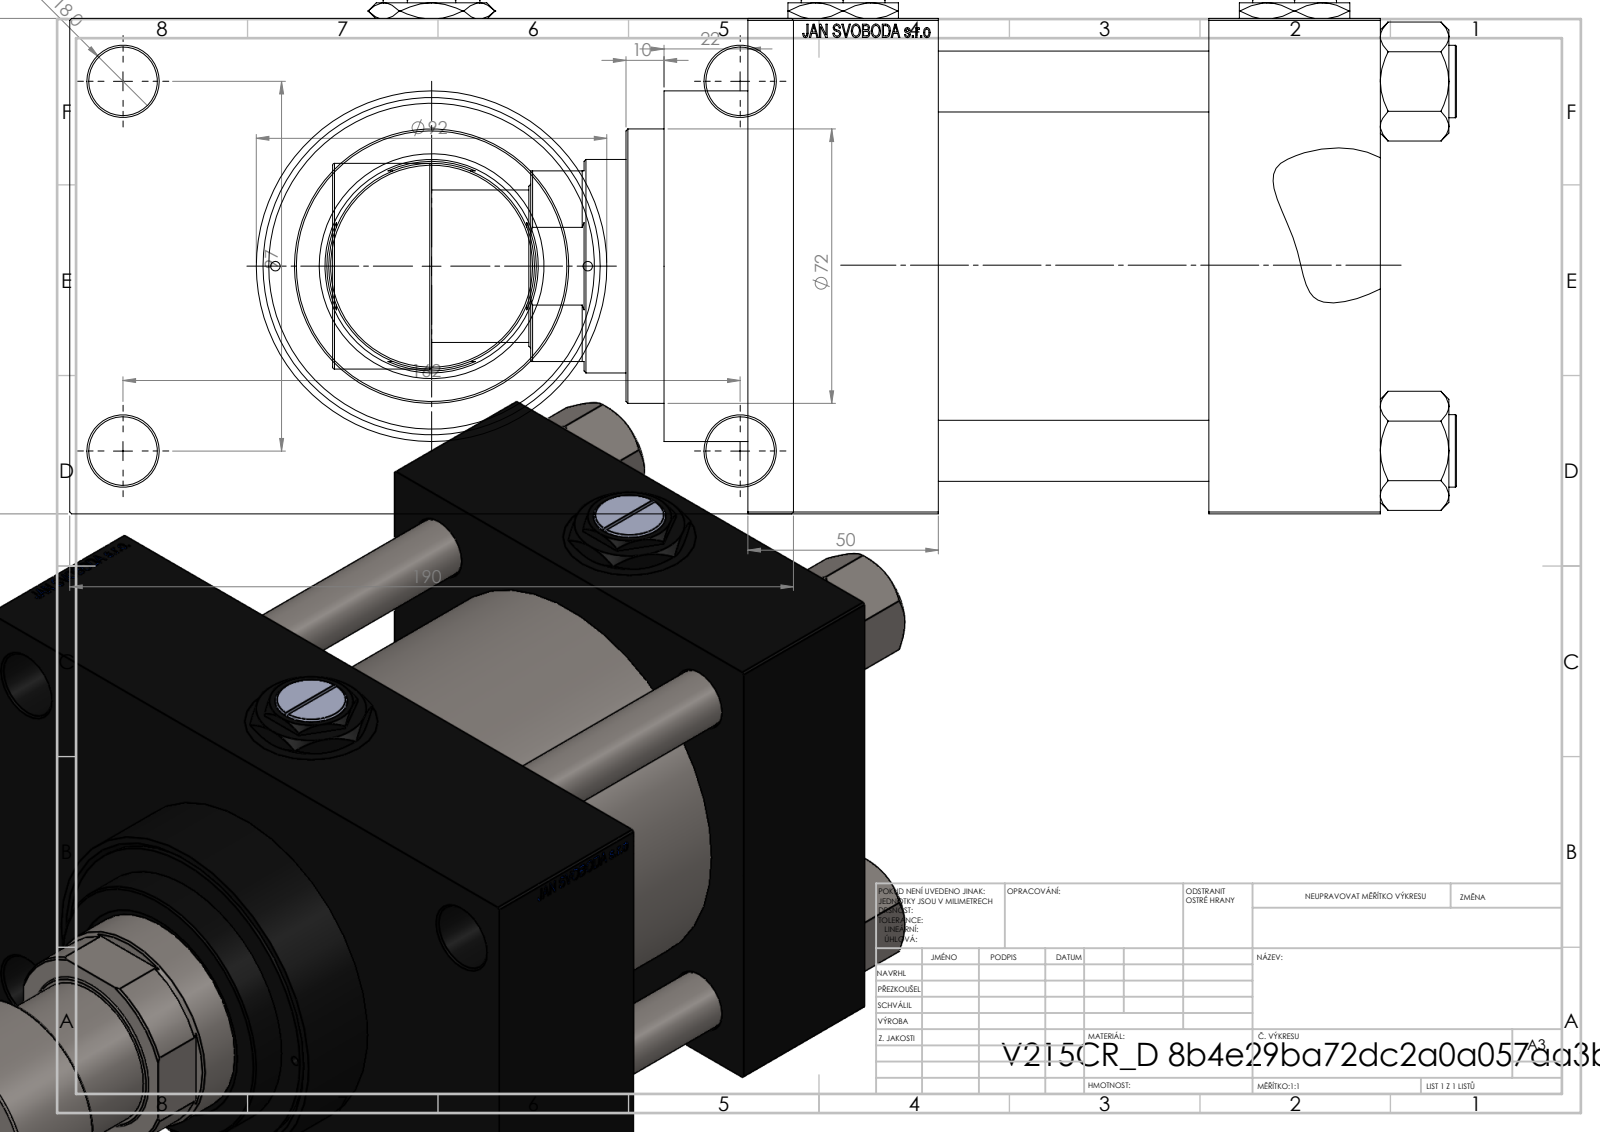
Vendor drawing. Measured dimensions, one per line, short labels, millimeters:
name: Zatka_pro_OIL_PORT; V215CR_D_Body; V215CR_VCP_D; V215CR_D_TYCINKA (+3 more)
written by: SolidWorks 2019 (CONFIG_CONTROL_DESIGN)
unit: mm
bodies: 14 solids, 1274 faces (599 planar, 107 cylindrical, 568 other)
size: 295 × 190 × 137
volume: 2 706 000 mm³; area: 381 668 mm²
holes: 4× ⌀16, 4× ⌀18, 4× ⌀26.44, 4× ⌀35, 3× ⌀7, 2× ⌀2.5, 1× ⌀40.5, 1× ⌀56, 1× ⌀59, 1× ⌀76, 1× ⌀85.5, 1× ⌀100
bosses: 4× ⌀19, 1× ⌀106, 1× ⌀92, 1× ⌀72, 1× ⌀54, 1× ⌀40
face distances: 130, 116, 50, 45, 71, 166, 121, 30, 160, 51
hole spacings: 32.55, 49.02, 62.87, 68.52, 94.41, 96.9, 101.73, 102.27
